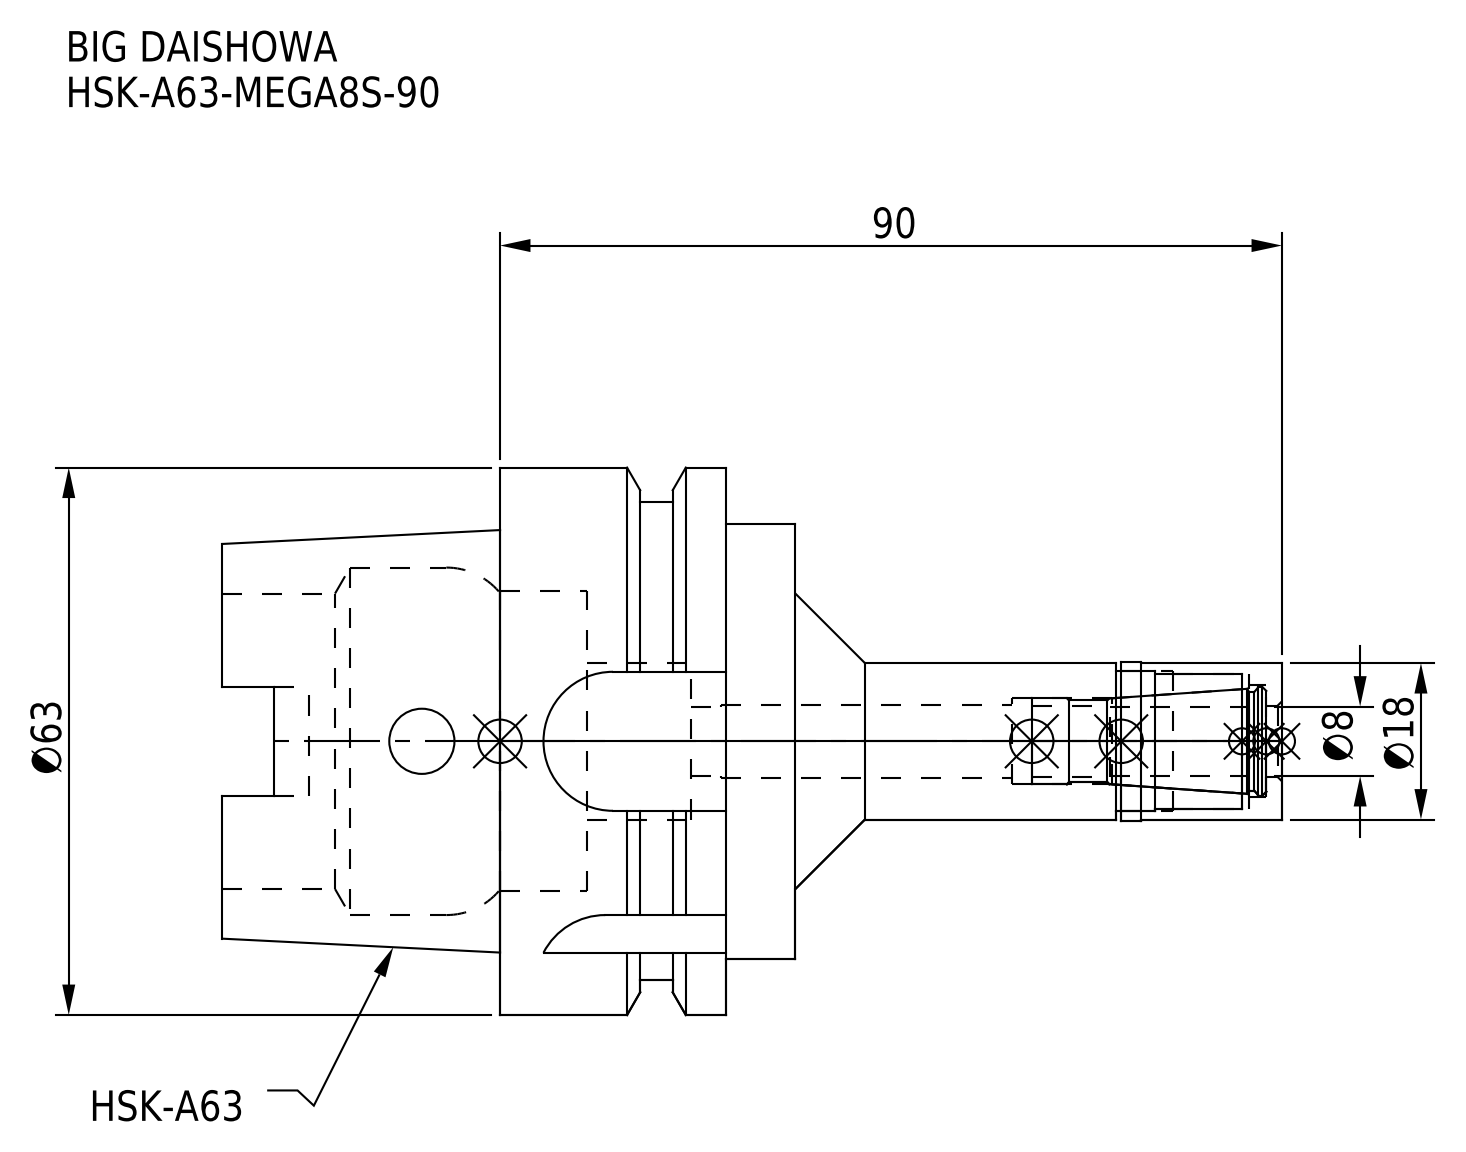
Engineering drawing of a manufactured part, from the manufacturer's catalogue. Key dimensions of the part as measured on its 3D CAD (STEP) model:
Part name (STEP PRODUCT): HSK-A63-MEGA8S-90-080-FreeParts; HSK-A63-MEGA8S-90_1.stp; DXF_TEMP_ASSY_ASM_4_ASM.stp; HSK-A63-MEGA8S-90 (+3 more)
STEP written by: SolidWorks 2019 (CONFIG_CONTROL_DESIGN)
Units: millimetres
Bodies: 2 solids, 122 faces (47 planar, 55 cylindrical, 20 other)
Overall size (bounding box): 122 × 63 × 63
Volume: 109 239 mm³ · Surface area: 30 207 mm²
Round holes (diameter × count): ⌀7.5 ×1, ⌀8 ×1, ⌀8.2 ×1, ⌀8.4 ×1, ⌀9.9 ×1, ⌀12.9 ×1, ⌀15.6 ×1, ⌀16.1 ×1, ⌀34 ×1, ⌀34.5 ×1, ⌀40 ×1
Round bosses / shafts (diameter × count): ⌀63 ×1, ⌀55 ×1, ⌀50 ×1, ⌀18.3 ×1, ⌀18 ×1
Partial cylindrical surfaces — rounded edges, fillets, slot ends (radius × count): R2.88 ×4, R8 ×4
Main face-to-face distances: 26, 34, 8, 24.05, 16.05, 9.95, 66, 58, 41.95, 32
